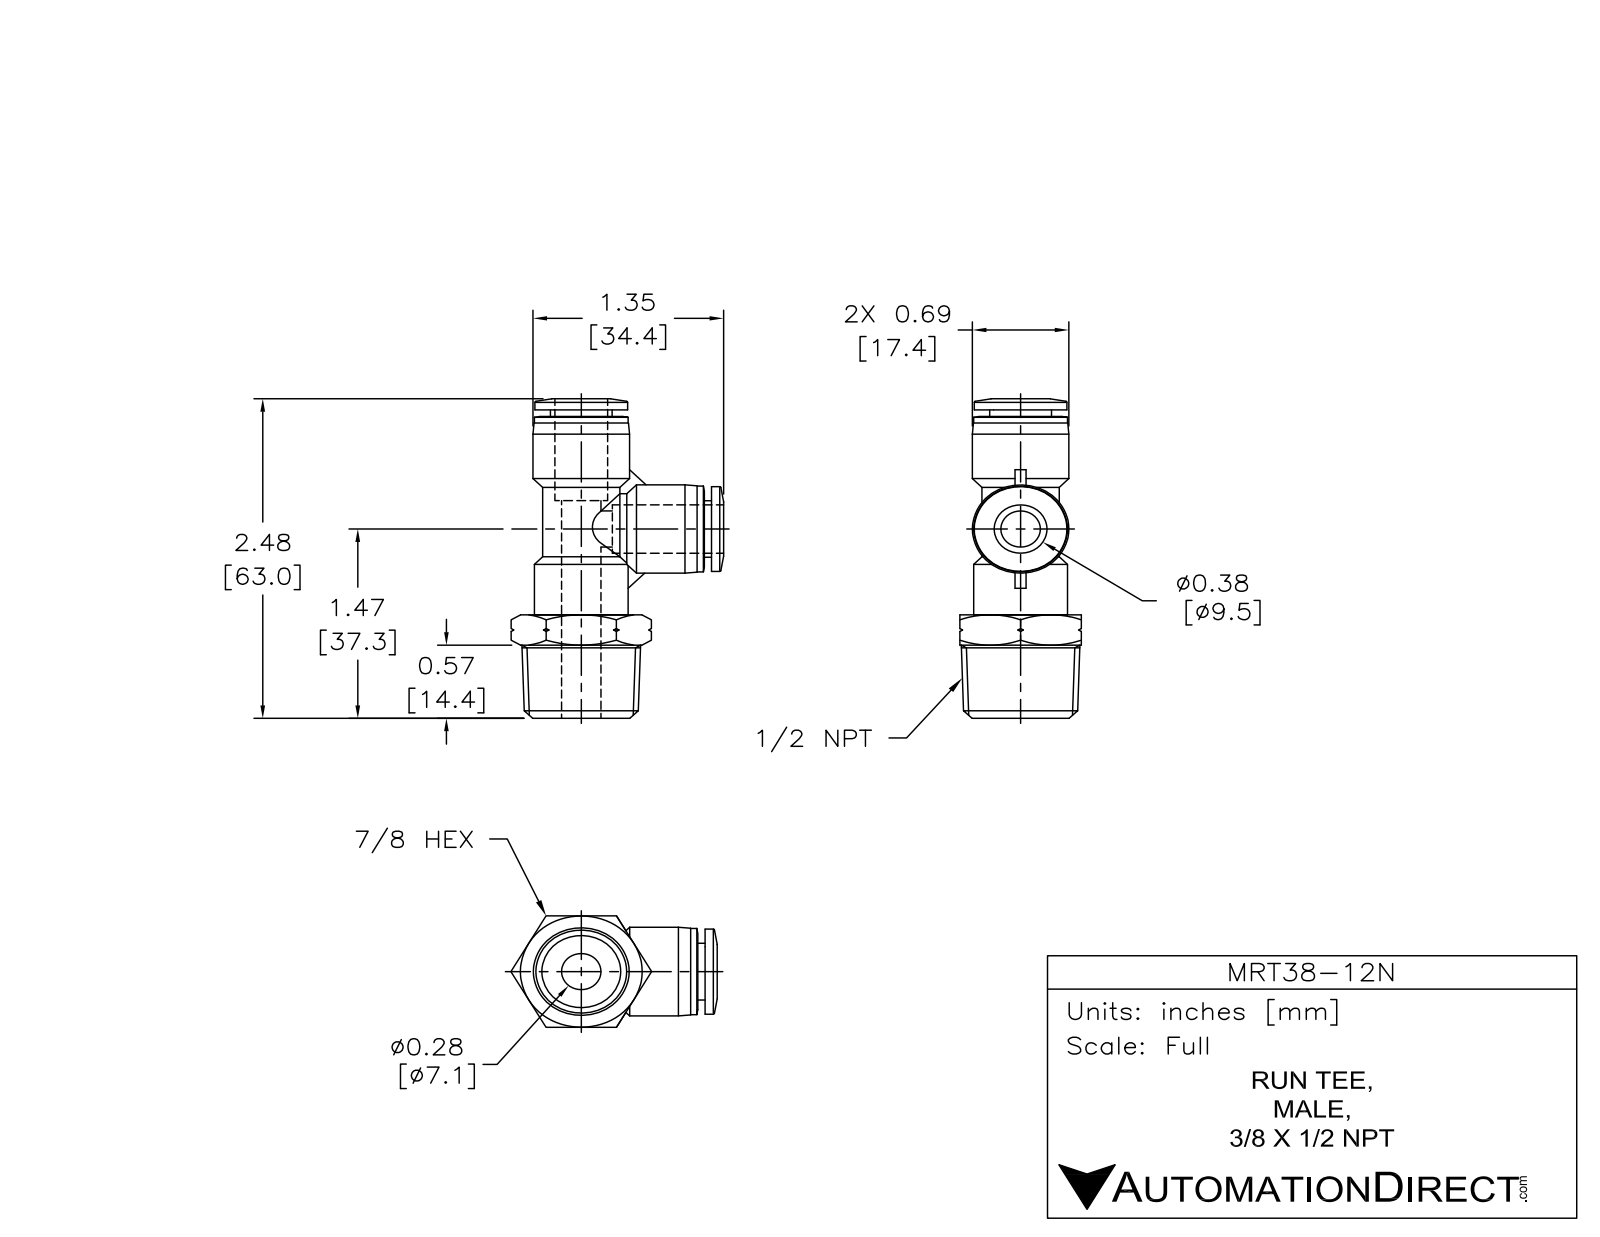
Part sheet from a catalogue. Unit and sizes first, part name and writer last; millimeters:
Units: millimetres
Overall size (bounding box): 63.3 × 38.5 × 22
Round holes (diameter × count): ⌀8 ×2, ⌀9.8 ×2, ⌀7 ×1
Round bosses / shafts (diameter × count): ⌀17.5 ×2, ⌀17 ×2, ⌀16.8 ×2, ⌀14 ×2, ⌀11.2 ×2
Main face-to-face distances: 22, 20.5, 1.3, 61.1, 40.6, 59.8, 39.3, 16.6, 17.9, 10
Volume: 15 100 mm³ · Surface area: 8 039 mm²
Bodies: 1 solid, 121 faces (24 planar, 33 cylindrical, 64 other)
Part name (STEP PRODUCT): MRT38-12N
STEP written by: SolidWorks 2015 (AUTOMOTIVE_DESIGN)
